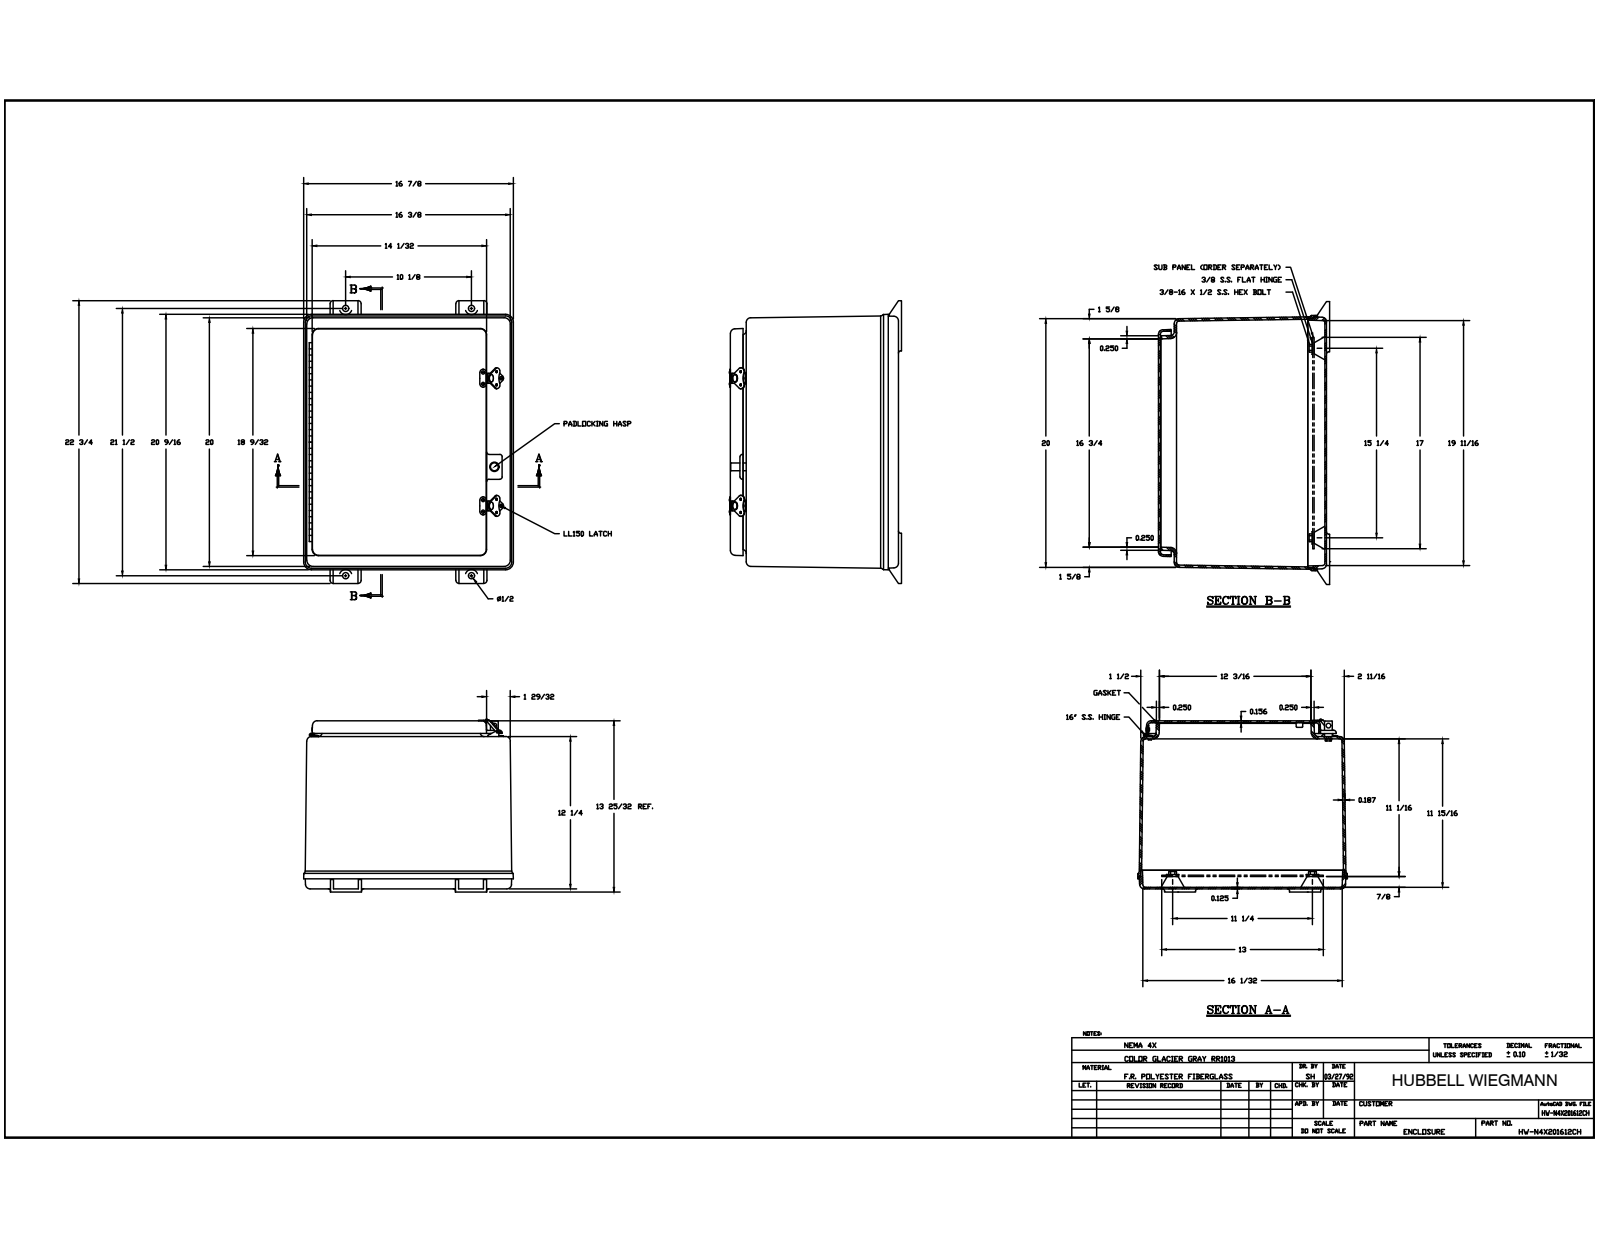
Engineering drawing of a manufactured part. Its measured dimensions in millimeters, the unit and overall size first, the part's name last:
Units: millimetres
Overall size (bounding box): 577.85 × 428.62 × 354.46
Round holes (diameter × count): ⌀3.3 ×20, ⌀1.59 ×8, ⌀1.65 ×8, ⌀3.5 ×4, ⌀4.76 ×4, ⌀14.3 ×4, ⌀3.68 ×2, ⌀7.14 ×2, ⌀12.95 ×2, ⌀12.96 ×2, ⌀3.17 ×1, ⌀3.43 ×1
Round bosses / shafts (diameter × count): ⌀7.54 ×8, ⌀3.56 ×8, ⌀12.7 ×2, ⌀6.35 ×1, ⌀5.11 ×1, ⌀5.08 ×1
Partial cylindrical surfaces — rounded edges, fillets, slot ends (radius × count): R0.25 ×59, R4.76 ×25, R6.35 ×24, R12.7 ×12, R7.94 ×10, R9.53 ×10, R0.76 ×8, R2.54 ×5
Main face-to-face distances: 4.75, 3.18, 3.97, 343.71, 340.53, 339.74, 336.56, 306.39, 303.21, 33.35
Hole centre spacings: 260.35, 120.65, 139.7, 381, 38.78, 80.66, 260.34, 282.84
Volume: 5 121 000 mm³ · Surface area: 2 370 000 mm²
Bodies: 38 solids, 1111 faces (430 planar, 430 cylindrical, 251 other)
Part name (STEP PRODUCT): WPN201612SHWT; WPN2016B; WPN201612HWTPCVR; N201612G (+8 more)
STEP written by: Autodesk Inventor 2014 (AUTOMOTIVE_DESIGN)
